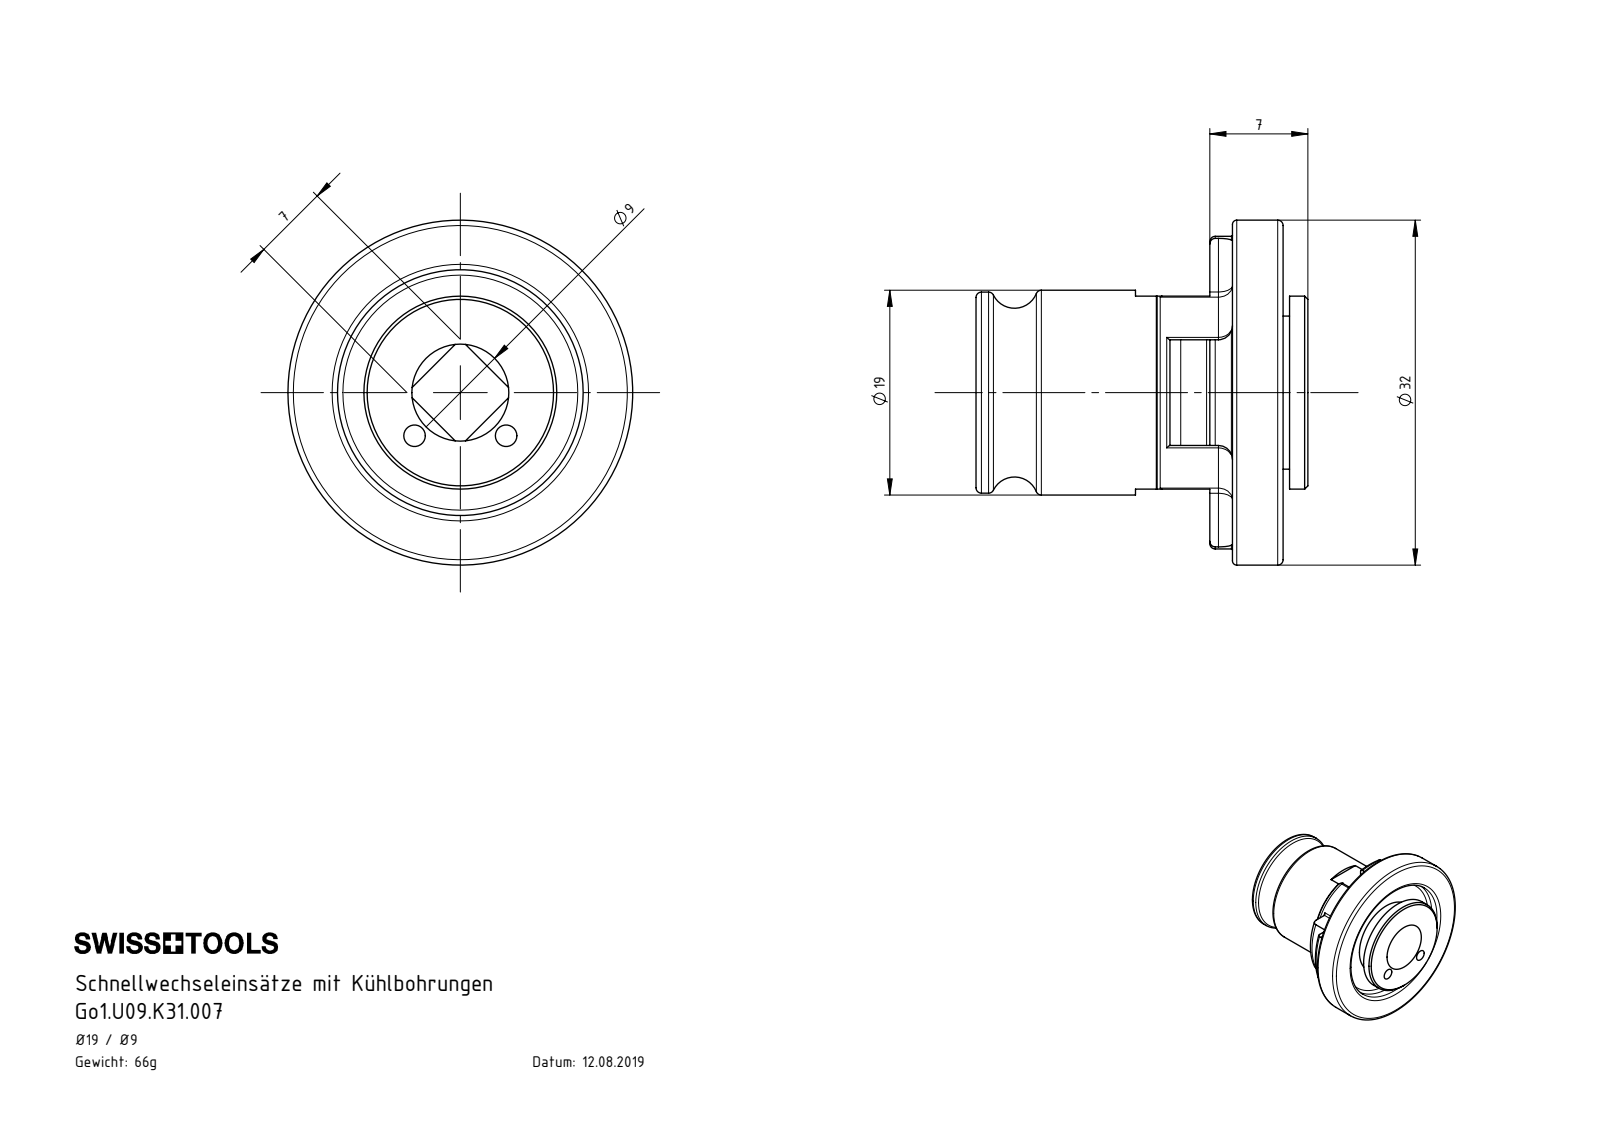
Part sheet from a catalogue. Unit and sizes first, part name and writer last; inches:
Units: inches
Overall size (bounding box): 1.26 × 1.26 × 1.213
Round holes (diameter × count): ⌀0.079 ×2, ⌀0.354 ×1, ⌀0.449 ×1, ⌀0.898 ×1
Round bosses / shafts (diameter × count): ⌀1.26 ×1, ⌀0.748 ×1, ⌀0.734 ×1, ⌀0.729 ×1, ⌀0.705 ×1, ⌀0.559 ×1
Partial cylindrical surfaces — rounded edges, fillets, slot ends (radius × count): R0.02 ×8, R0.051 ×4, R0.488 ×1, R0.571 ×1
Main face-to-face distances: 0.093, 0.185, 0.276, 0.183, 0.091, 0.937, 1.03, 1.122, 1.213, 1.146
Hole centre spacings: 0.23, 0.335
Volume: 0.515 in³ · Surface area: 7.967 in²
Bodies: 1 solid, 114 faces (36 planar, 34 cylindrical, 44 other)
Part name (STEP PRODUCT): Go1.U09.K31.007
STEP written by: SolidWorks 2017 (AUTOMOTIVE_DESIGN)
